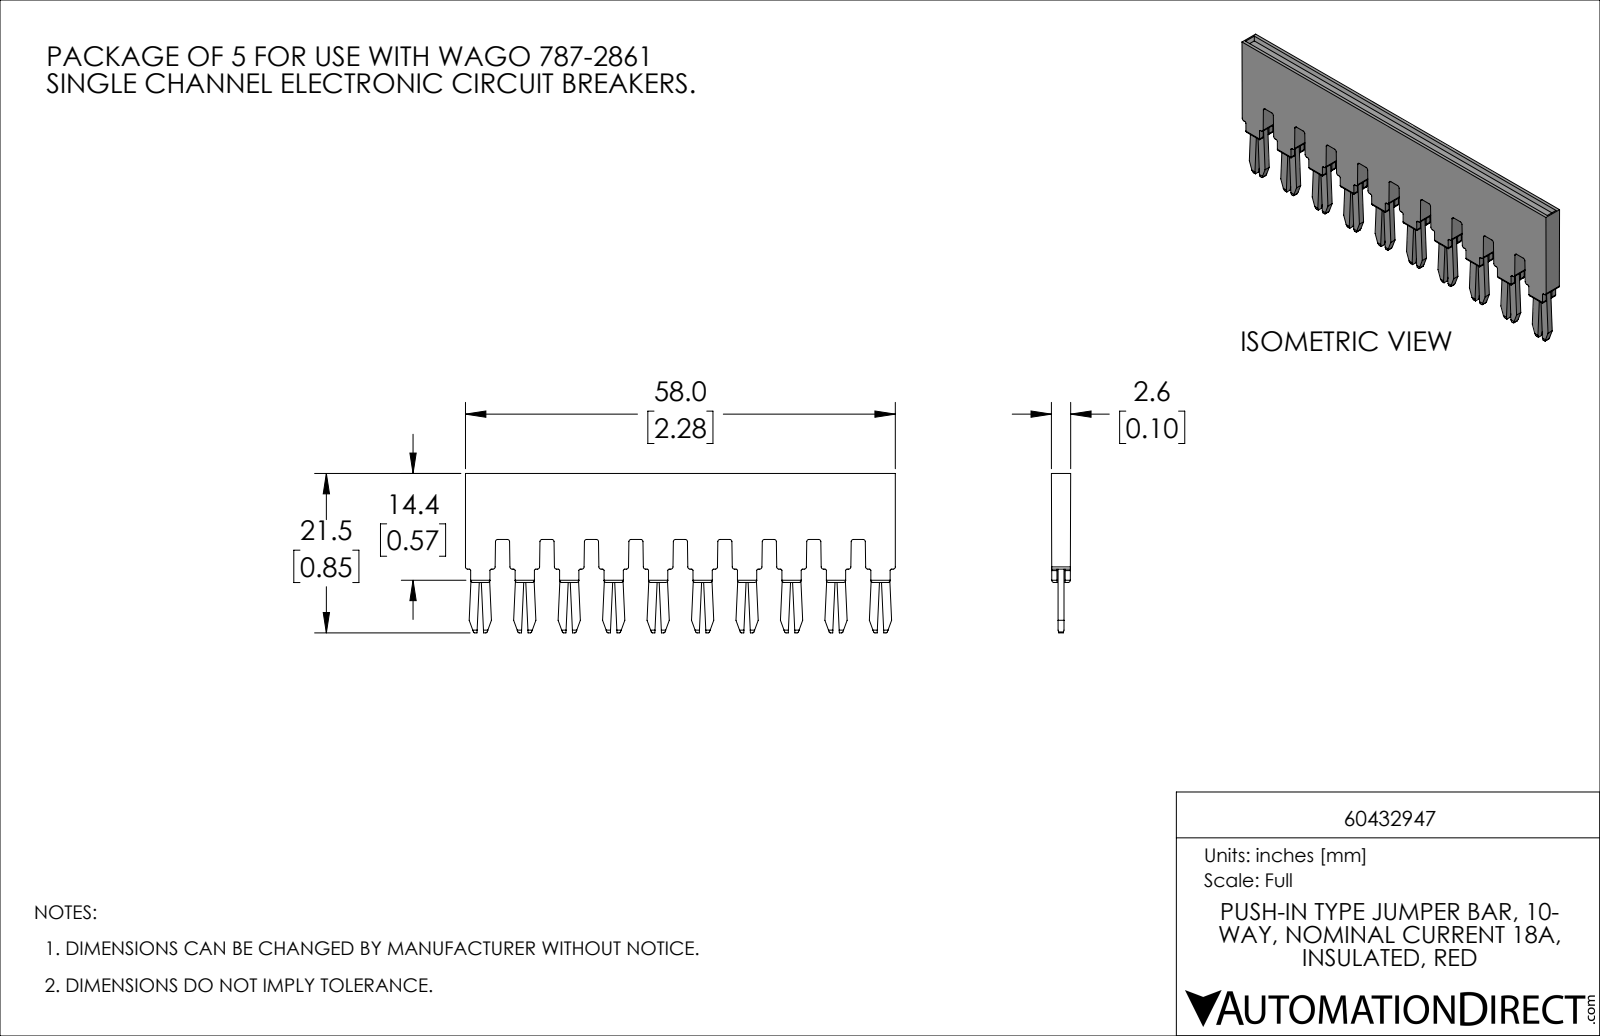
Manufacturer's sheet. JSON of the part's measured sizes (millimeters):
{"part_name": "60432947", "step_written_by": "SolidWorks 2019 (AUTOMOTIVE_DESIGN)", "units": "millimeters", "bodies": {"solids": 1, "faces": 445, "planar": 287, "cylindrical": 158, "other": 0}, "overall_size": [58, 21.5, 2.6], "volume_mm3": 1900, "surface_area_mm2": 2772, "partial_cylinders_radius": [[0.3, 60], [0.2, 40]], "face_to_face_distances": [6, 0.8, 12, 12, 18, 18, 6, 30, 24, 24]}
